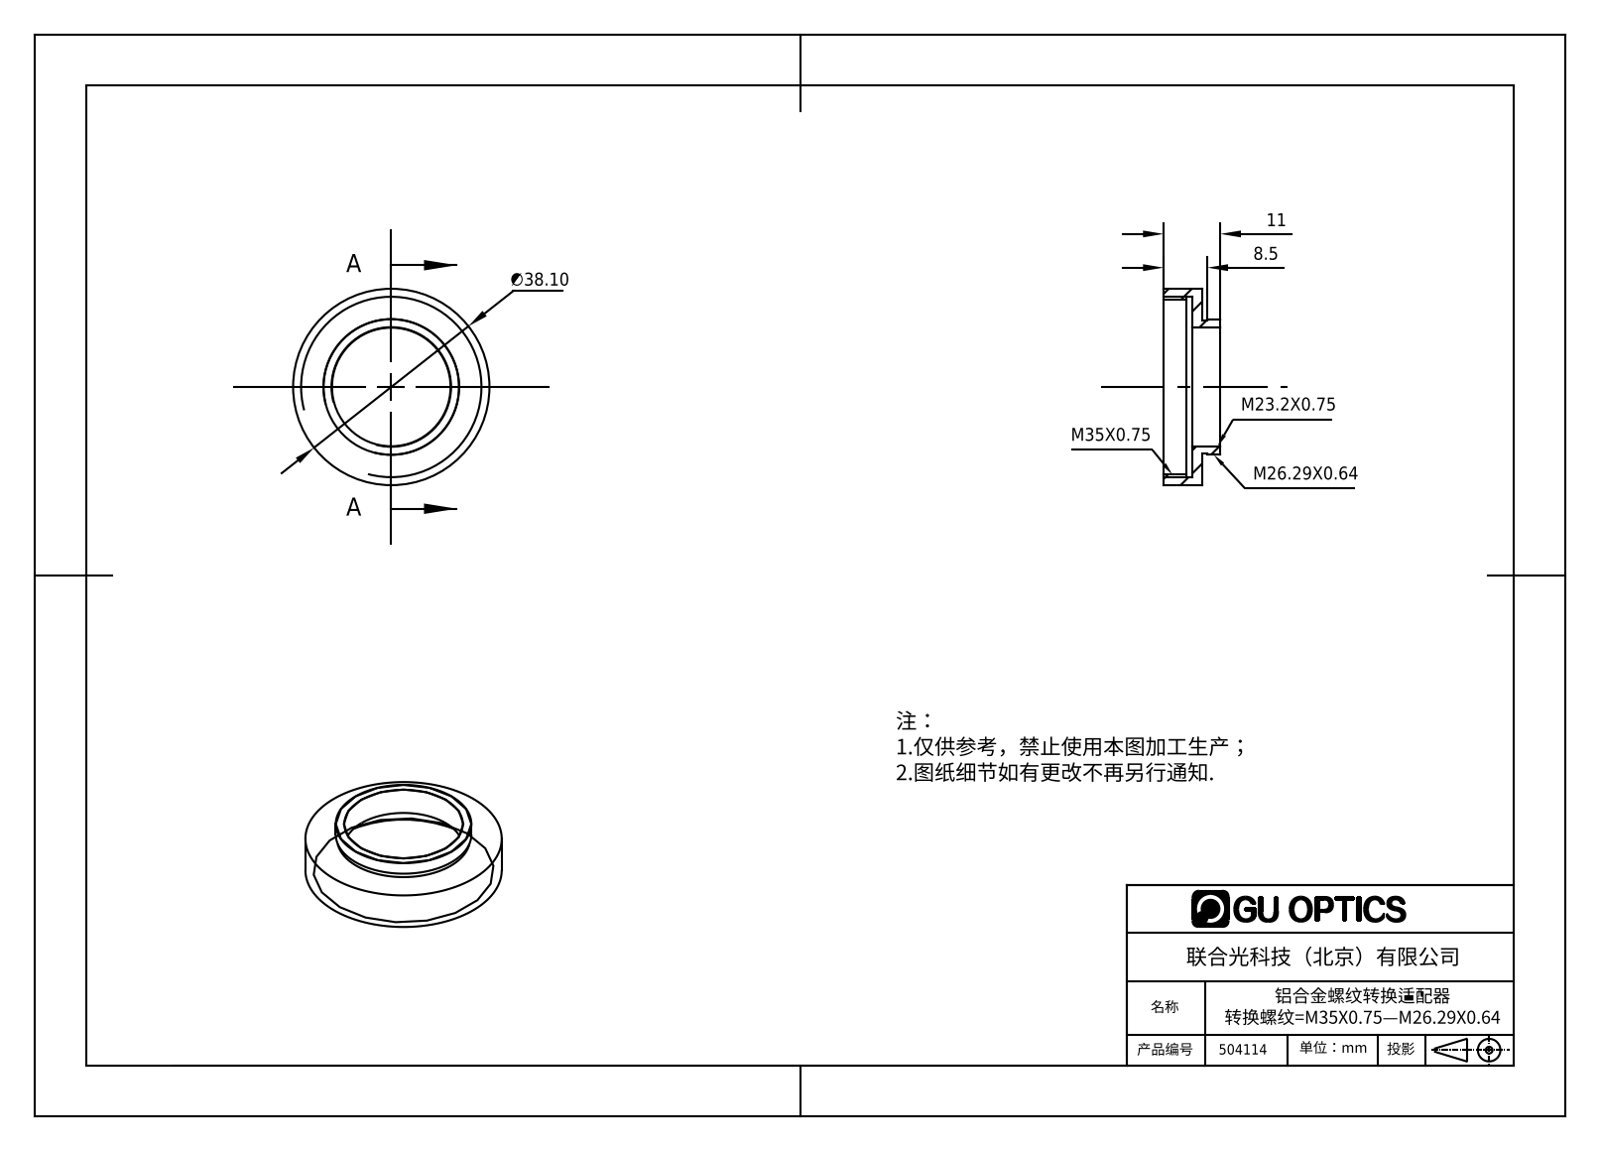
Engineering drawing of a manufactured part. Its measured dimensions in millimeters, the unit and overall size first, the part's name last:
Units: millimetres
Overall size (bounding box): 38.1 × 38.1 × 11
Round holes (diameter × count): ⌀23 ×1, ⌀34 ×1, ⌀35.2 ×1
Round bosses / shafts (diameter × count): ⌀38.1 ×1, ⌀26.32 ×1, ⌀25.8 ×1
Main face-to-face distances: 2, 5.5, 7.5, 11, 3.5, 1, 3, 4.5, 6.5, 8.5
Volume: 3 090 mm³ · Surface area: 3 796 mm²
Bodies: 1 solid, 18 faces (6 planar, 12 cylindrical, 0 other)
Part name (STEP PRODUCT): 504114
STEP written by: SolidWorks 2016 (AUTOMOTIVE_DESIGN)
